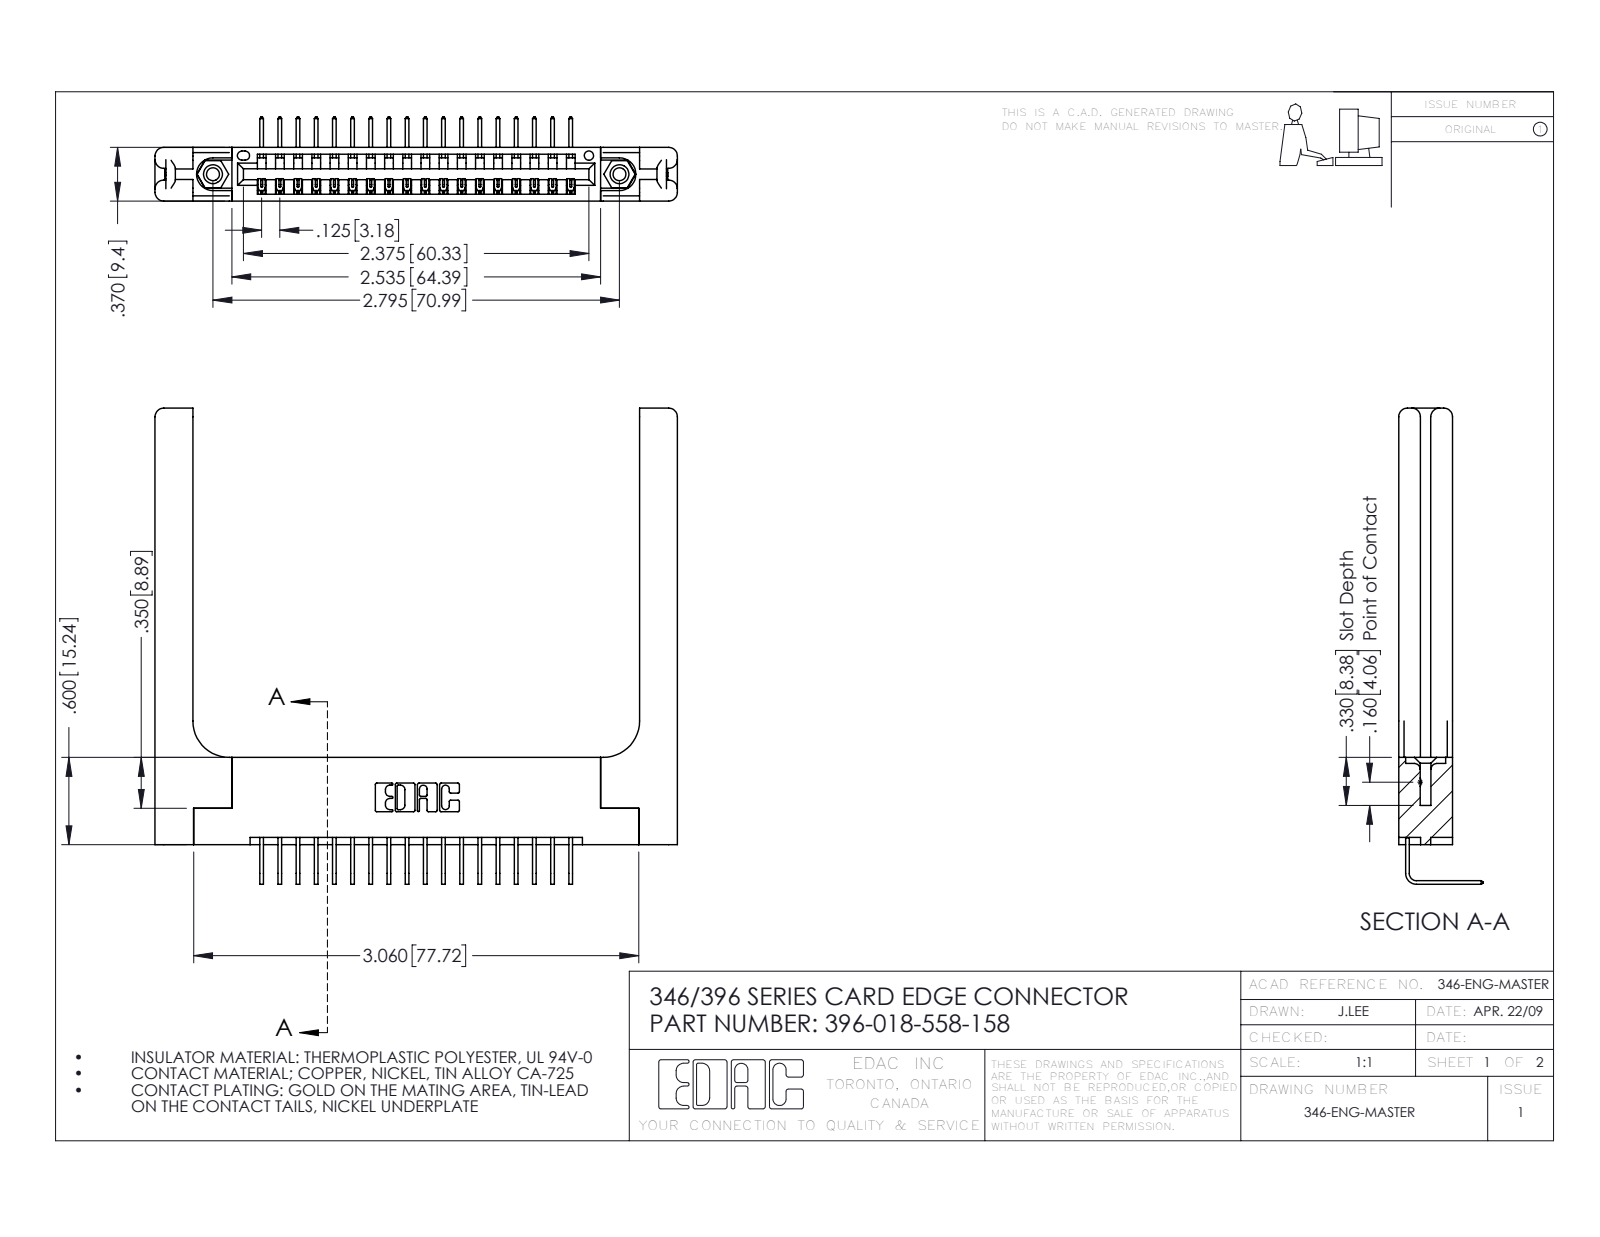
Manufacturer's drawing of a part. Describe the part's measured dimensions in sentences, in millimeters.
The part is named "345-250-001_345-250-001-102; 345-292-001_558 Tail - 2; 396-018-558-158; 346 Part_Flush Mounting Lugs - 0.156 Dia-TH (+1 more)". Its 3-D file was written by "SolidWorks 2016 (CONFIG_CONTROL_DESIGN)". It is 23 solids with 1458 faces: 980 planar, 418 cylindrical and 60 other. Overall it measures 91.2 by 83.1 by 14.7 millimeters. Its volume is 16 100 cubic millimeters and its surface area 16 050 square millimeters. Round holes: 2 of diameter 2.3, 2 of diameter 3.2, 2 of diameter 4, 1 of diameter 1.6. Round bosses or shafts: 2 of diameter 3.9. Partial cylindrical surfaces (rounded edges, fillets, slot ends): 36 of radius 0.2, 22 of radius 0.3, 16 of radius 1.5, 6 of radius 0.2, 6 of radius 0.8, 3 of radius 0.7, 2 of radius 0.8, 2 of radius 0.8. The main face-to-face distances are 9.4, 3.8, 1.8, 8.2, 3.8, 1.2, 6.4, 0.6, 7.6, 2.6. The hole center spacings are 6.2, 65.7, 71.
